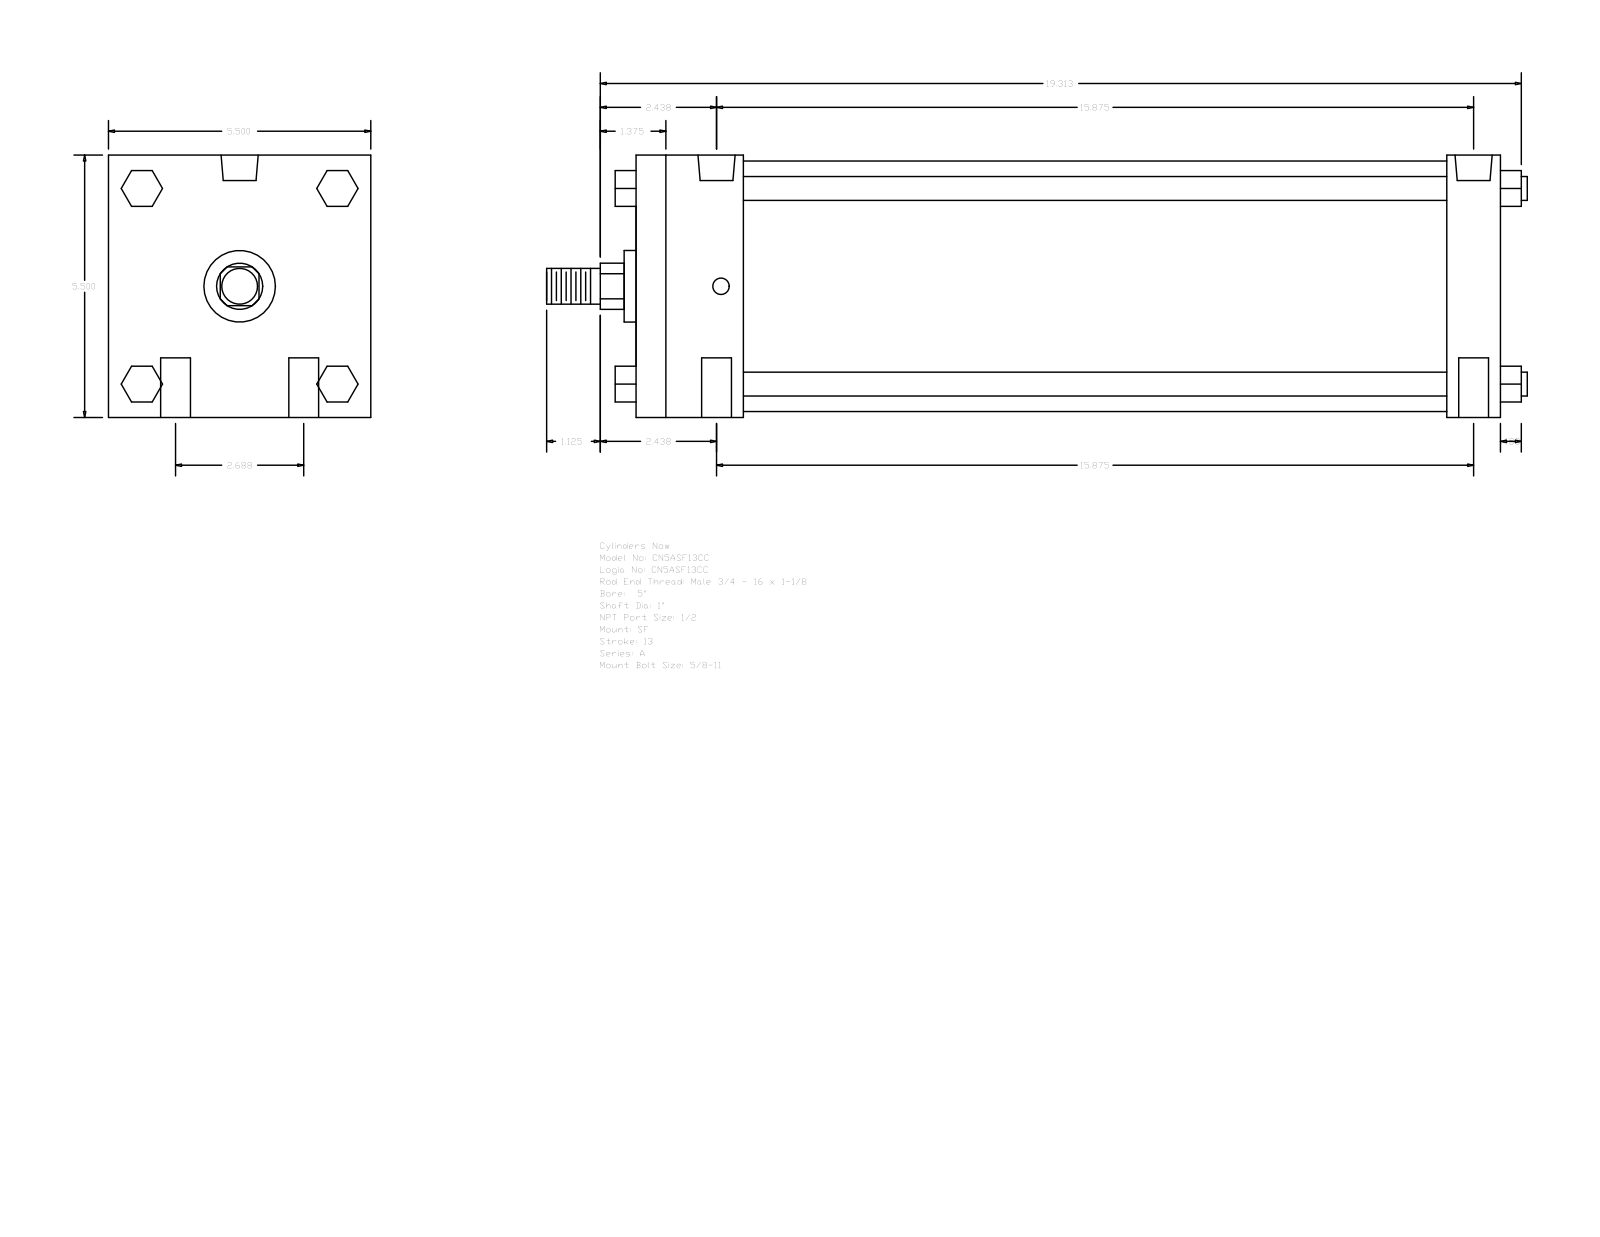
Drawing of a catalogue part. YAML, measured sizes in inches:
part_name: "A_SF__0500_1"
step_written_by: "GSSL Pune (CONFIG_CONTROL_DESIGN)"
units: inches
bodies: {solids: 0, faces: 124, planar: 94, cylindrical: 30, other: 0}
overall_size: [20.563, 5.5, 5.5]
round_holes:
  - {diameter: 0.625, count: 4}
  - {diameter: 0.344, count: 2}
  - {diameter: 0.778, count: 2}
round_bosses_or_shafts:
  - {diameter: 0.5, count: 4}
  - {diameter: 5.25, count: 1}
  - {diameter: 1.5, count: 1}
  - {diameter: 1, count: 1}
  - {diameter: 0.75, count: 1}
partial_cylinders:
  - {radius: 0.484, count: 1}
face_to_face_distances: [5.5, 18.125, 2.25, 17, 14.75, 15.875, 1.125, 0.75, 2.05, 3.55]
hole_center_spacings: [1.344, 15.932, 15.875, 2.687, 16.101, 15.687]
